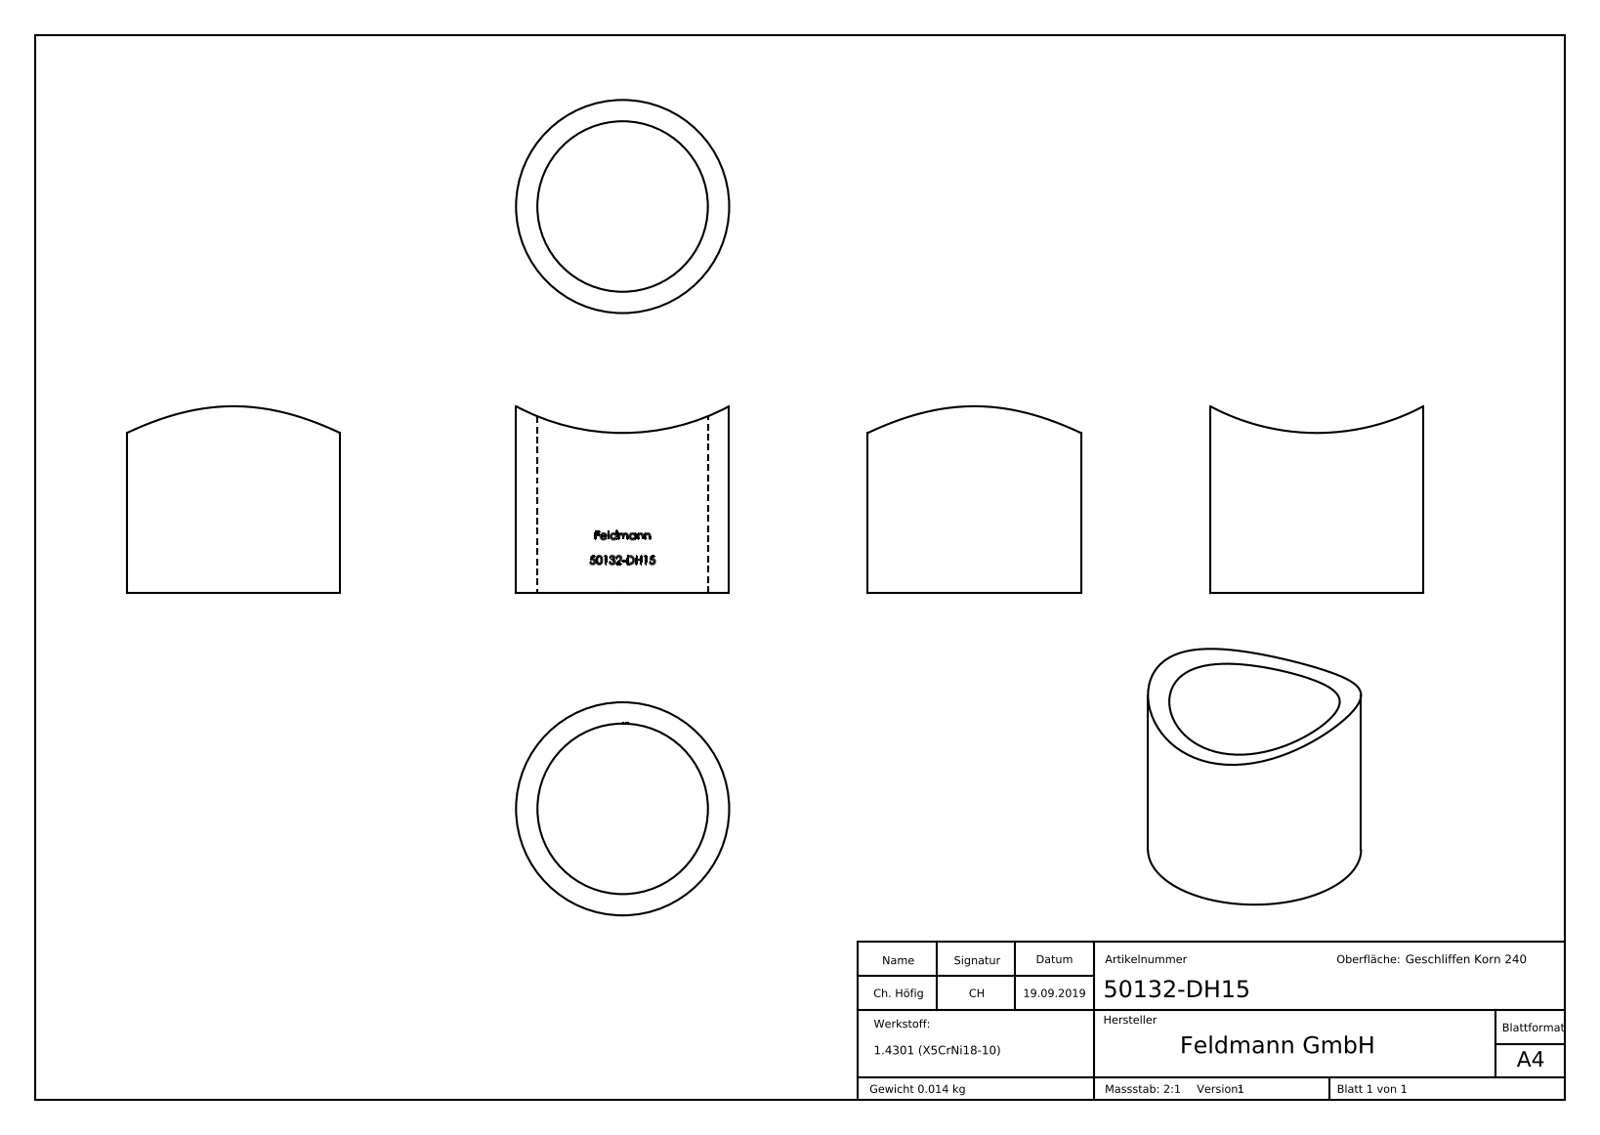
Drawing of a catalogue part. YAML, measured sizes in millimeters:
part_name: "50132-DH15"
step_written_by: "SolidWorks 2015 (CONFIG_CONTROL_DESIGN)"
units: millimeters
bodies: {solids: 1, faces: 240, planar: 110, cylindrical: 30, other: 100}
overall_size: [20, 20, 17.51]
volume: 1810
surface_area: 2051
round_holes:
  - {diameter: 16, count: 1}
round_bosses_or_shafts:
  - {diameter: 20, count: 1}
partial_cylinders:
  - {radius: 8.1, count: 1}
  - {radius: 21.2, count: 1}
face_to_face_distances: [1.78, 2.59, 2.77, 2.32, 0.45, 0.79, 0.83, 0.93, 2.84, 2.24]
